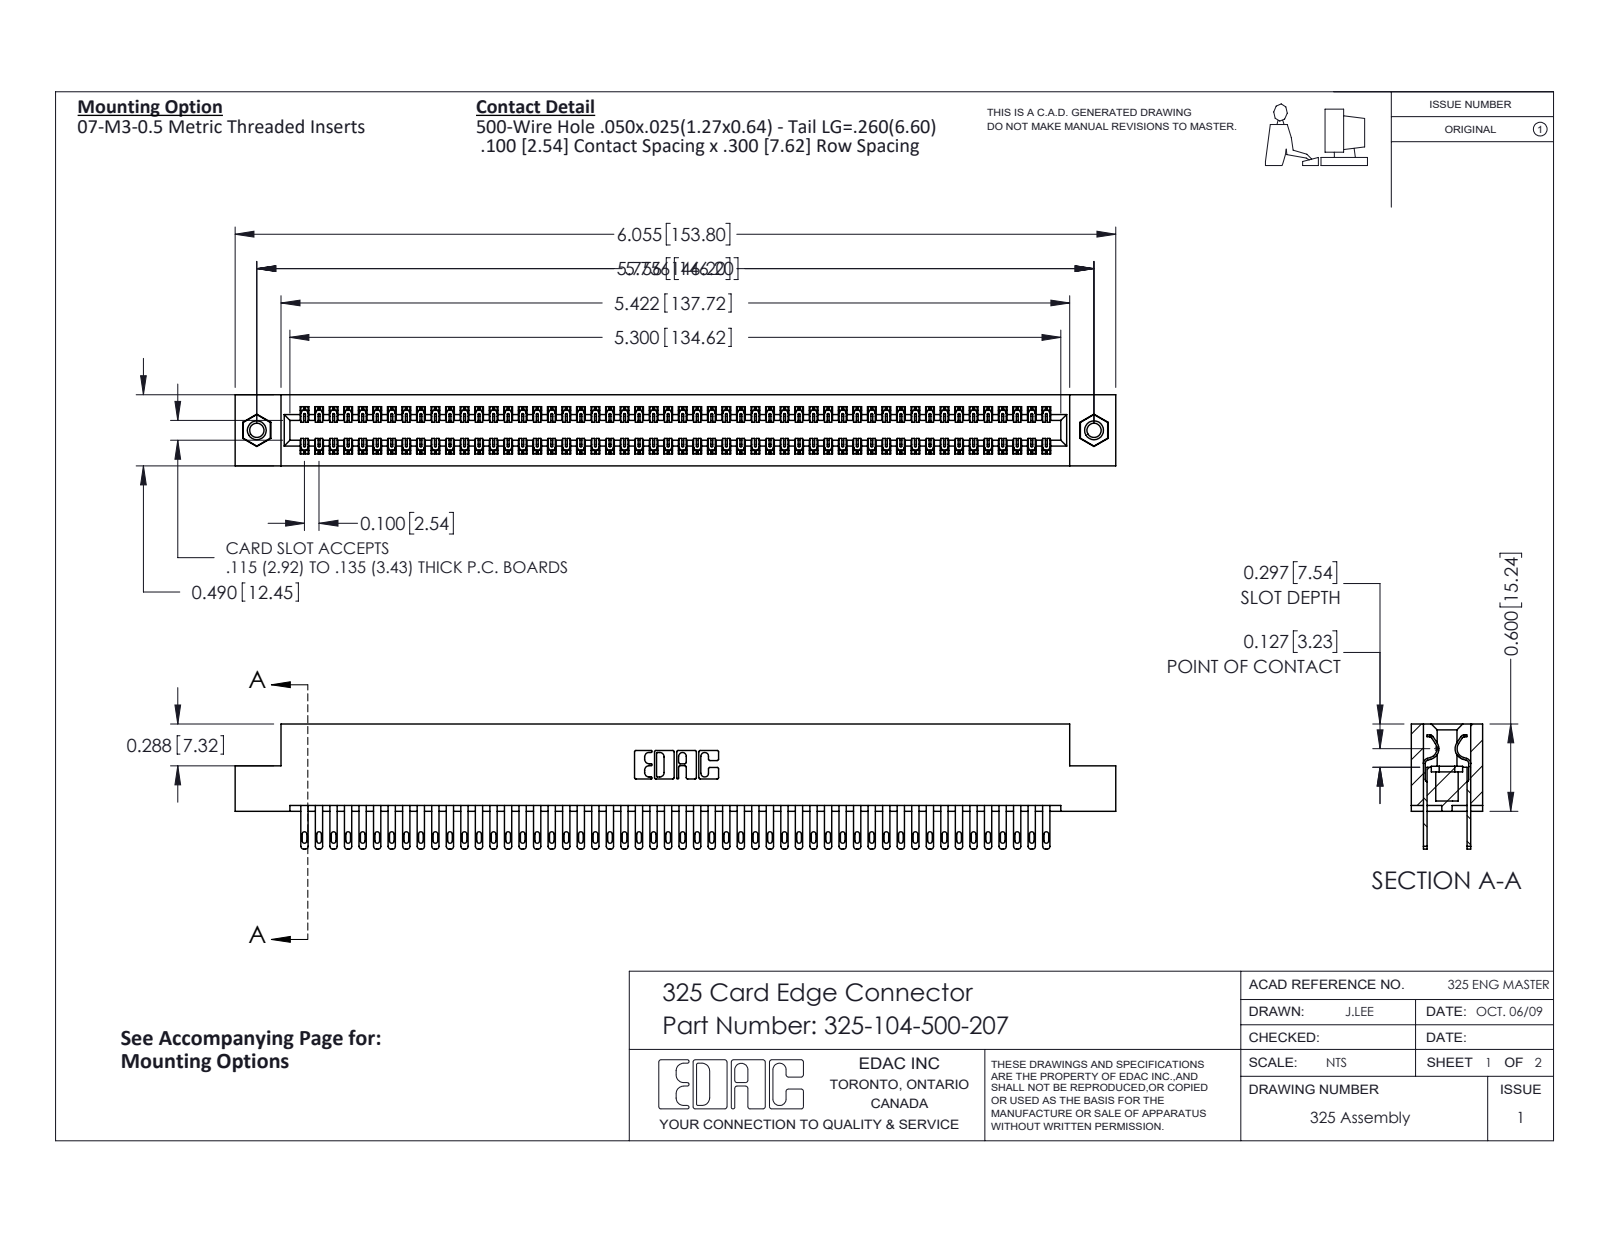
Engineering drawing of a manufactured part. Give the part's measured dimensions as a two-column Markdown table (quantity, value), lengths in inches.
| quantity | value |
| --- | --- |
| part name | 325-104-500-207; 345-250-001_345-250-005-103; 325-292-001_325-293-100; 325 Part_TI |
| STEP written by | SolidWorks 2016 (CONFIG_CONTROL_DESIGN) |
| units | inches |
| bodies | 107 solids, 5166 faces (3222 planar, 1928 cylindrical, 16 other) |
| overall size | 6.055 × 0.86 × 0.49 |
| volume | 1.236 in³ |
| surface area | 40.08 in² |
| round holes (diameter × count) | 0.098 × 2, 0.125 × 2, 0.16 × 2 |
| round bosses / shafts (diameter × count) | 0.155 × 2 |
| partial cylindrical surfaces (radius × count) | 0.006 × 156, 0.016 × 104, 0.02 × 104, 0.01 × 22, 0.007 × 6, 0.031 × 6, 0.026 × 3, 0.014 × 2 |
| main face-to-face distances | 0.083, 0.407, 0.3, 0.107, 0.383, 0.025, 0.49, 0.325, 0.275, 0.56 |
| hole center spacings | 5.756 |
